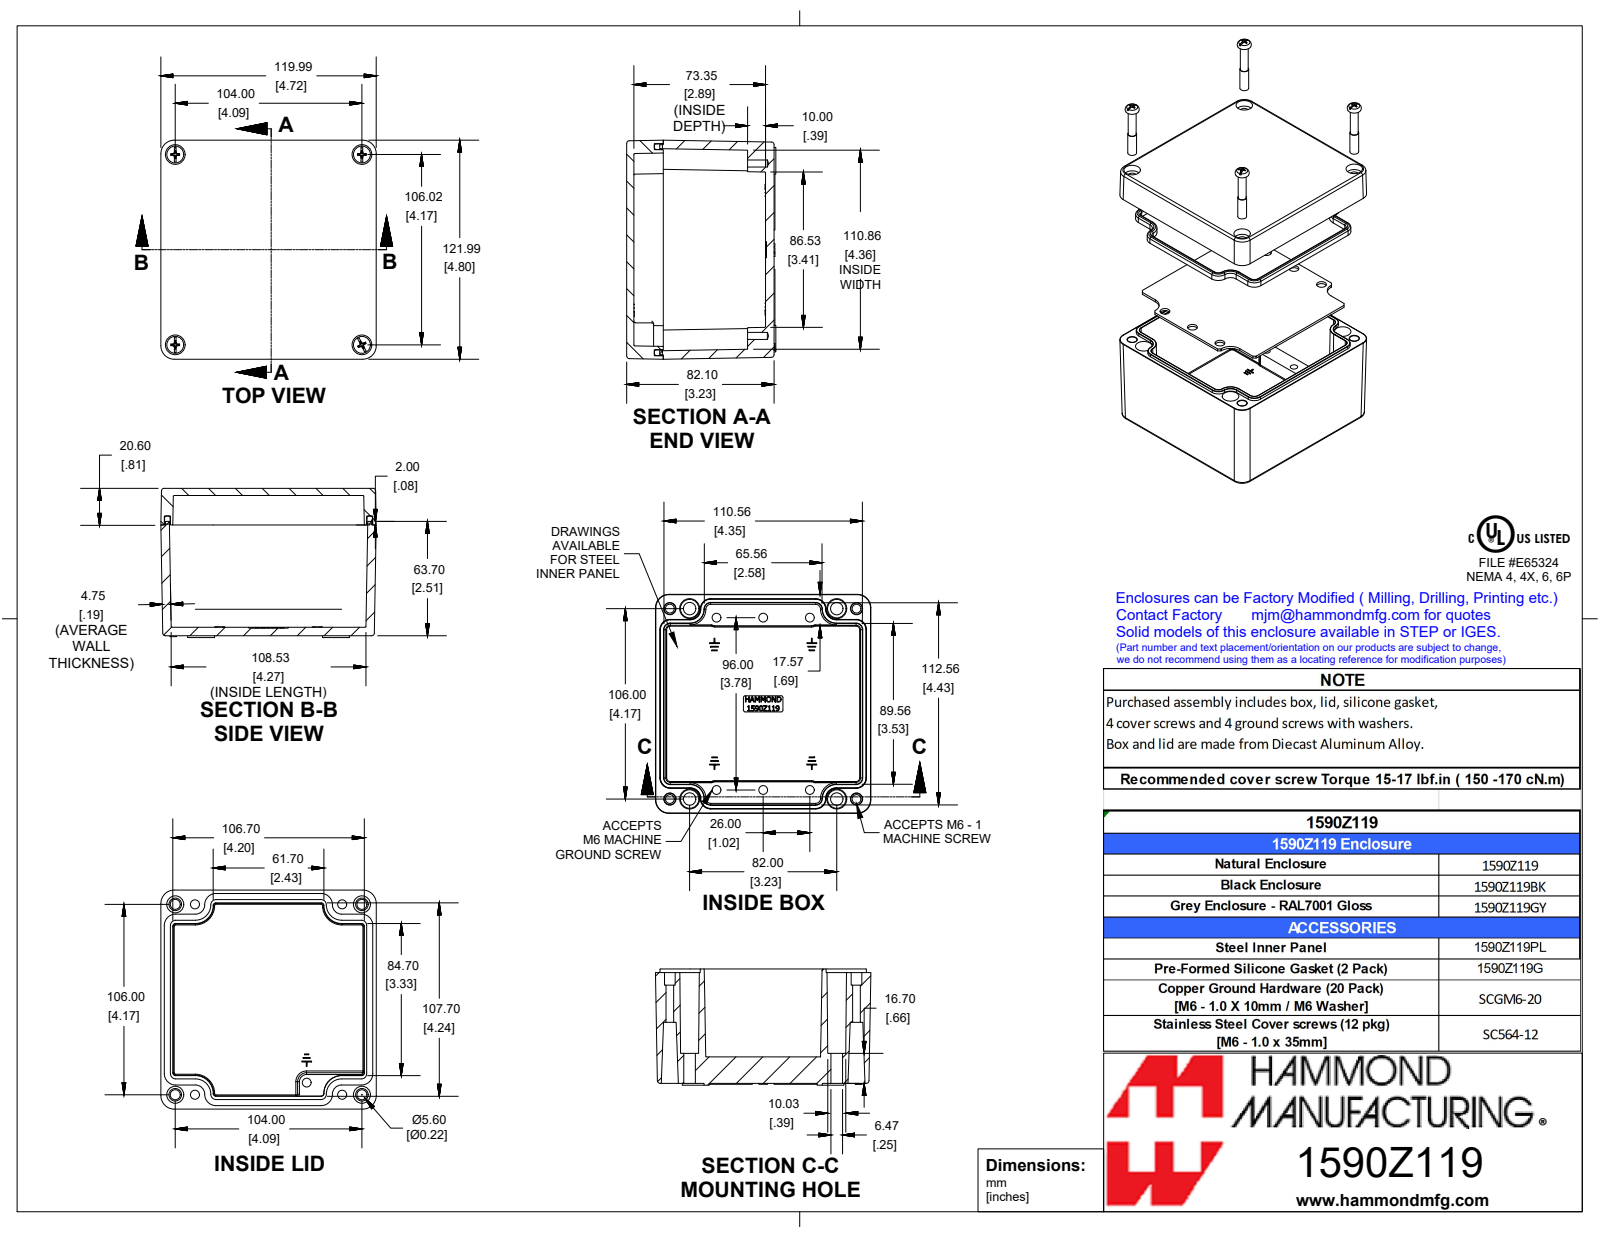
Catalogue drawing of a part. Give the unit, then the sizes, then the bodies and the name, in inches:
Units: inches
Overall size (bounding box): 4.803 × 4.724 × 3.272
Round holes (diameter × count): ⌀0.194 ×6, ⌀0.257 ×6, ⌀0.194 ×5, ⌀0.197 ×4, ⌀0.217 ×4, ⌀0.252 ×4, ⌀0.272 ×4, ⌀0.276 ×4, ⌀0.433 ×4
Round bosses / shafts (diameter × count): ⌀0.433 ×4, ⌀0.231 ×4, ⌀0.208 ×4
Partial cylindrical surfaces — rounded edges, fillets, slot ends (radius × count): R0.039 ×18, R0.008 ×16, R0.02 ×12, R0.059 ×8, R0.115 ×8, R0.249 ×8, R0.295 ×8, R0.01 ×4
Main face-to-face distances: 0.187, 3.232, 0.581, 2.652, 0.079, 0.659, 2.573, 3.075, 2.494, 2.415
Hole centre spacings: 1.024, 1.024, 3.897, 0.02, 3.76, 0.433, 0.622, 0.629
Volume: 22.74 in³ · Surface area: 275.6 in²
Bodies: 8 solids, 885 faces (421 planar, 163 cylindrical, 301 other)
Part name (STEP PRODUCT): 1590Z119
STEP written by: SolidWorks 2019 (CONFIG_CONTROL_DESIGN)
